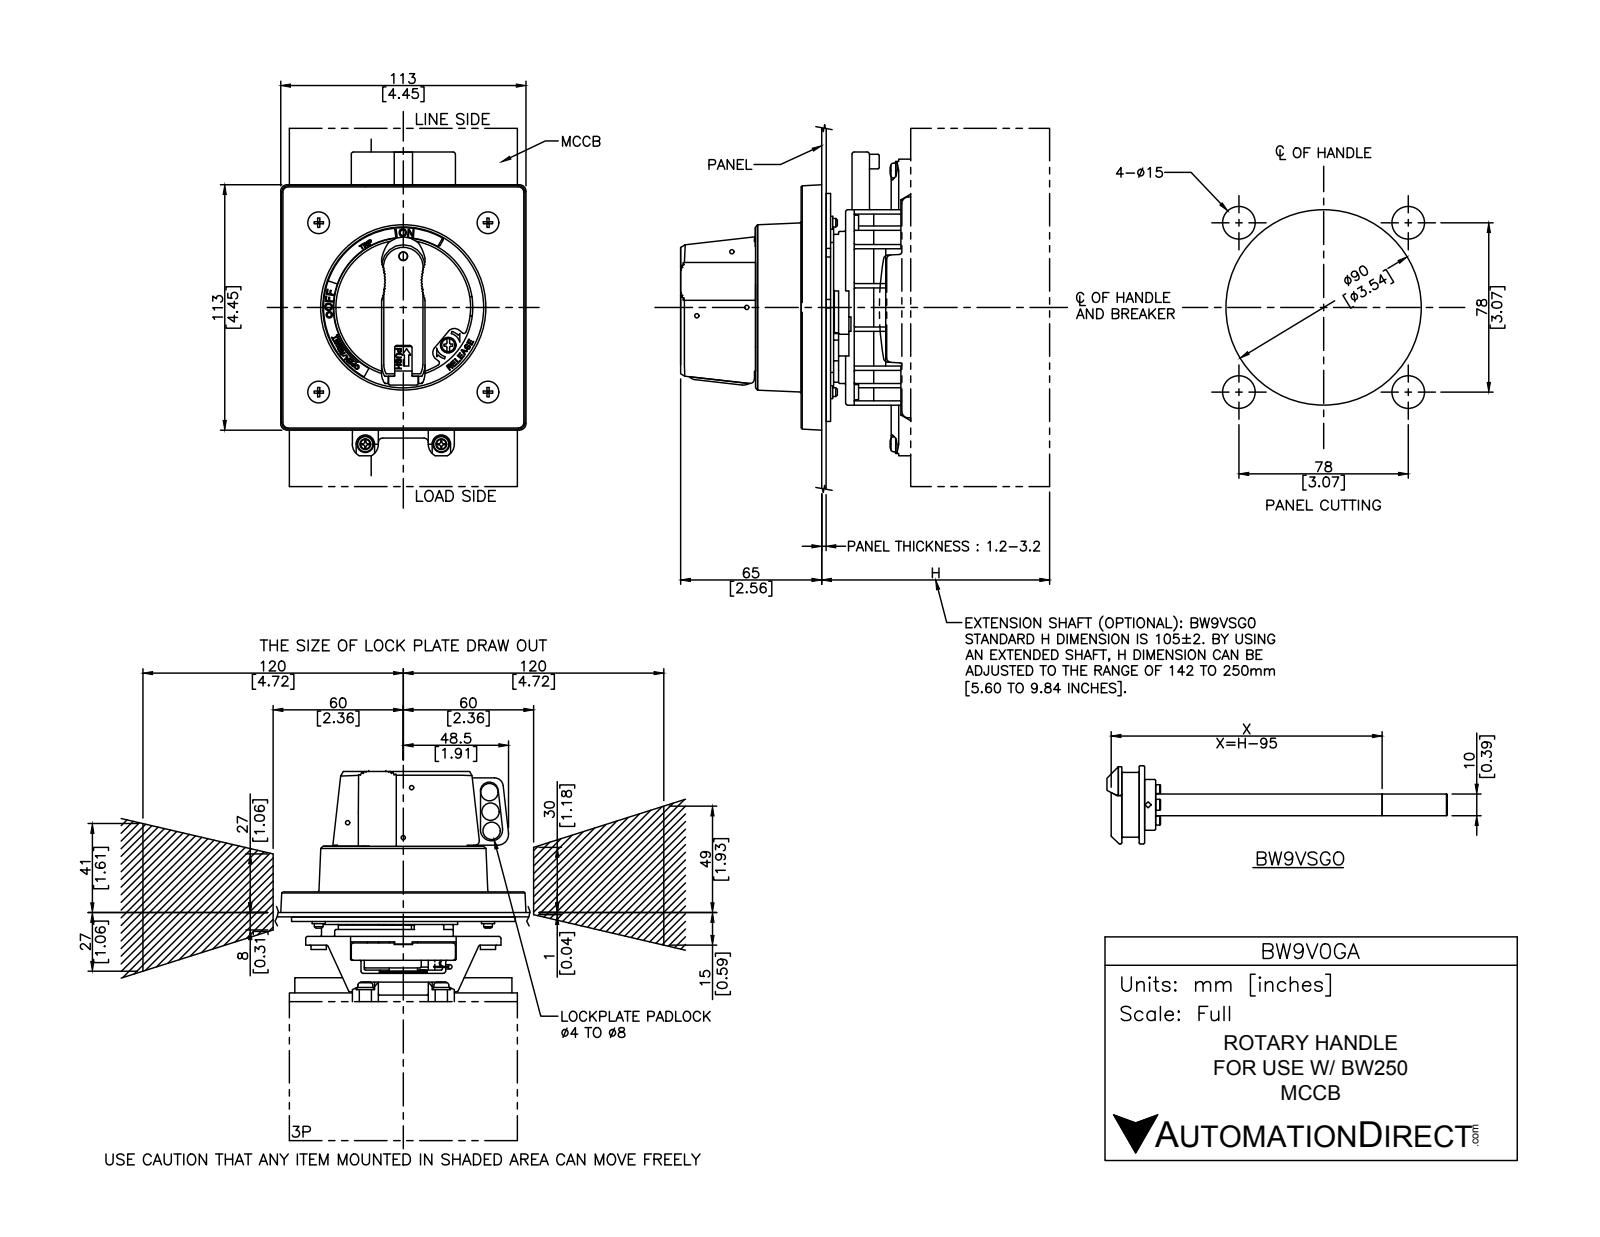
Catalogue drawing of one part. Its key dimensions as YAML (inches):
part_name: "BW9V0GA"
step_written_by: "SolidWorks 2018 (AUTOMOTIVE_DESIGN)"
units: inches
bodies: {solids: 12, faces: 189, planar: 87, cylindrical: 86, other: 16}
overall_size: [7.091, 5.378, 4.449]
volume: 24.85
surface_area: 157.1
round_holes:
  - {diameter: 0.157, count: 8}
  - {diameter: 2.52, count: 1}
  - {diameter: 2.992, count: 1}
round_bosses_or_shafts:
  - {diameter: 0.276, count: 8}
  - {diameter: 2.441, count: 1}
partial_cylinders:
  - {radius: 0.118, count: 8}
  - {radius: 0.236, count: 4}
  - {radius: 0.863, count: 2}
  - {radius: 0.397, count: 1}
face_to_face_distances: [0.535, 0.374, 0.161, 0.457, 0.079, 0.083, 0.453, 0.295, 1.024, 0.217]
hole_center_spacings: [1.269, 2.171, 2.417, 2.574, 3.071, 4.104, 4.591, 1.378]
